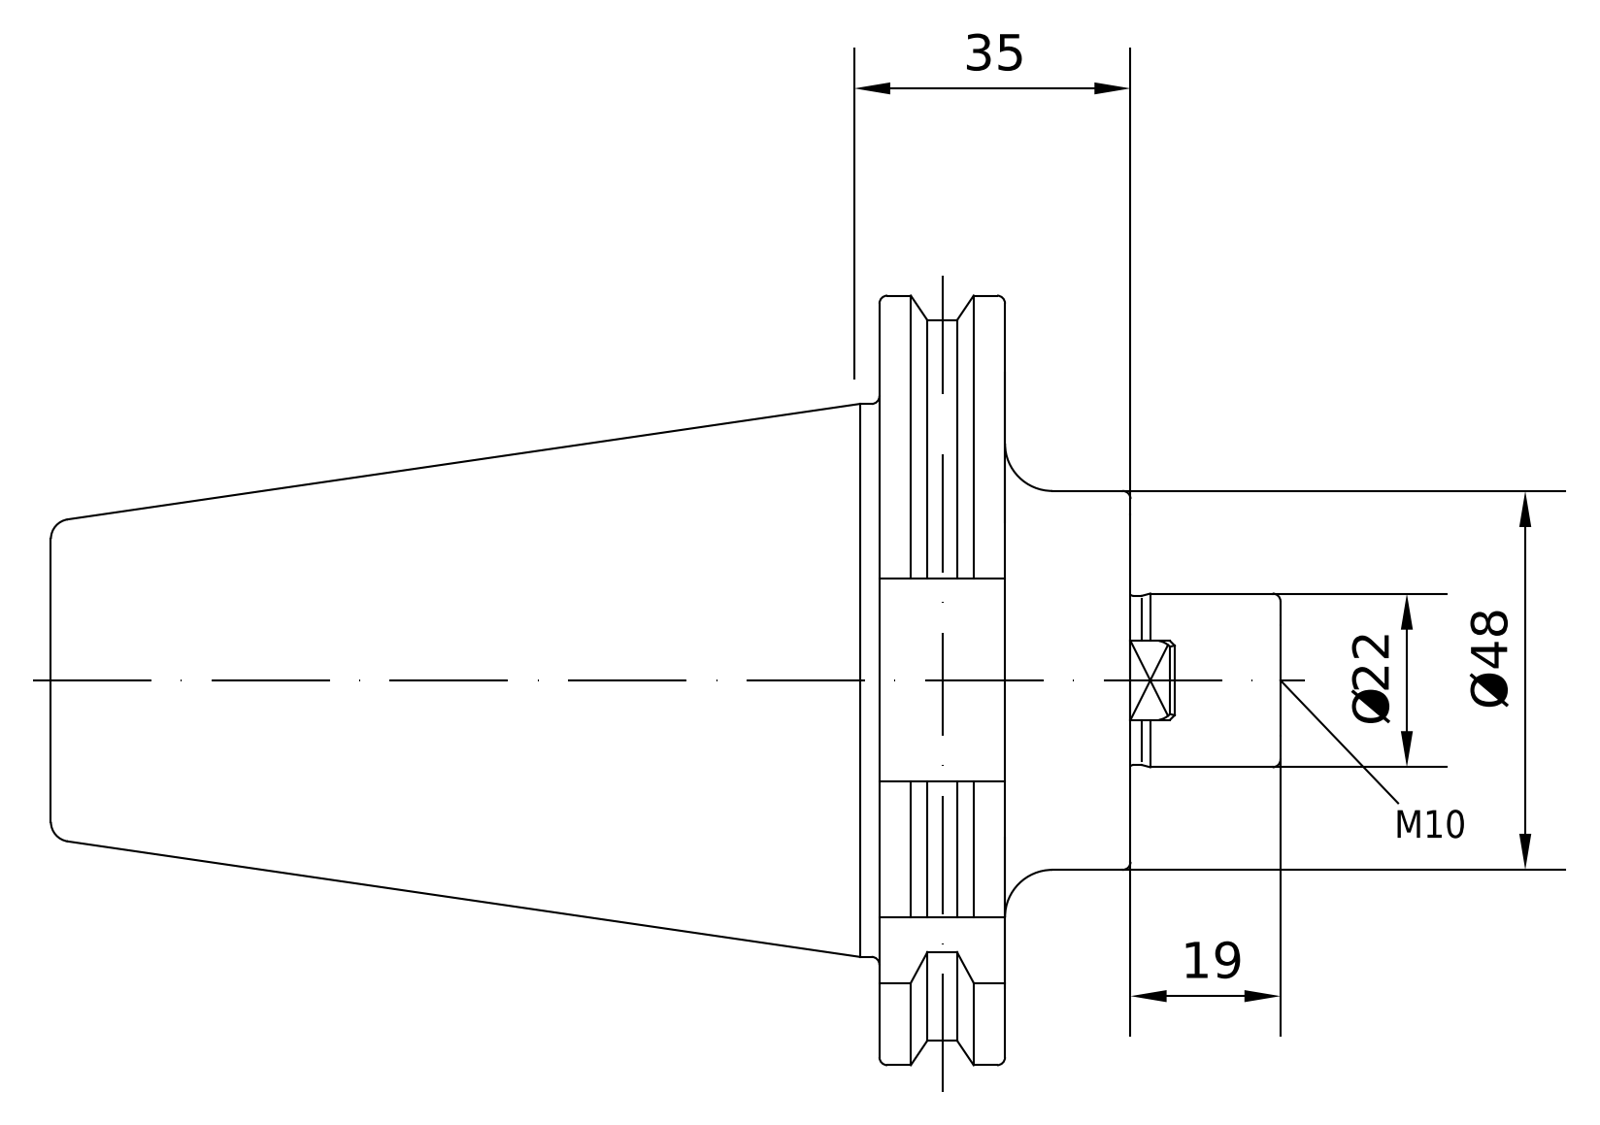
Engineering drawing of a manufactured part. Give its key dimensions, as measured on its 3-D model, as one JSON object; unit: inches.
{"part_name": "50-350-22", "step_written_by": "PRO/ENGINEER BY PARAMETRIC TECHNOLOGY CORPORATION, 2010430 (CONFIG_CONTROL_DESIGN)", "units": "inches", "bodies": {"solids": 1, "faces": 110, "planar": 32, "cylindrical": 28, "other": 50}, "overall_size": [6.126, 3.837, 3.701], "volume_in3": 22.94, "surface_area_in2": 74.19, "round_holes": [[0.335, 1], [0.394, 1], [0.817, 1], [0.985, 1], [1.012, 1]], "round_bosses_or_shafts": [[3.583, 1], [2.722, 1], [1.89, 1], [0.945, 1], [0.866, 1]], "partial_cylinders_radius": [[0.069, 1], [1.919, 1]], "face_to_face_distances": [0.624, 1.252, 0.628, 2.866, 4.126, 4.75, 5.378, 1.016, 6.126, 2]}
